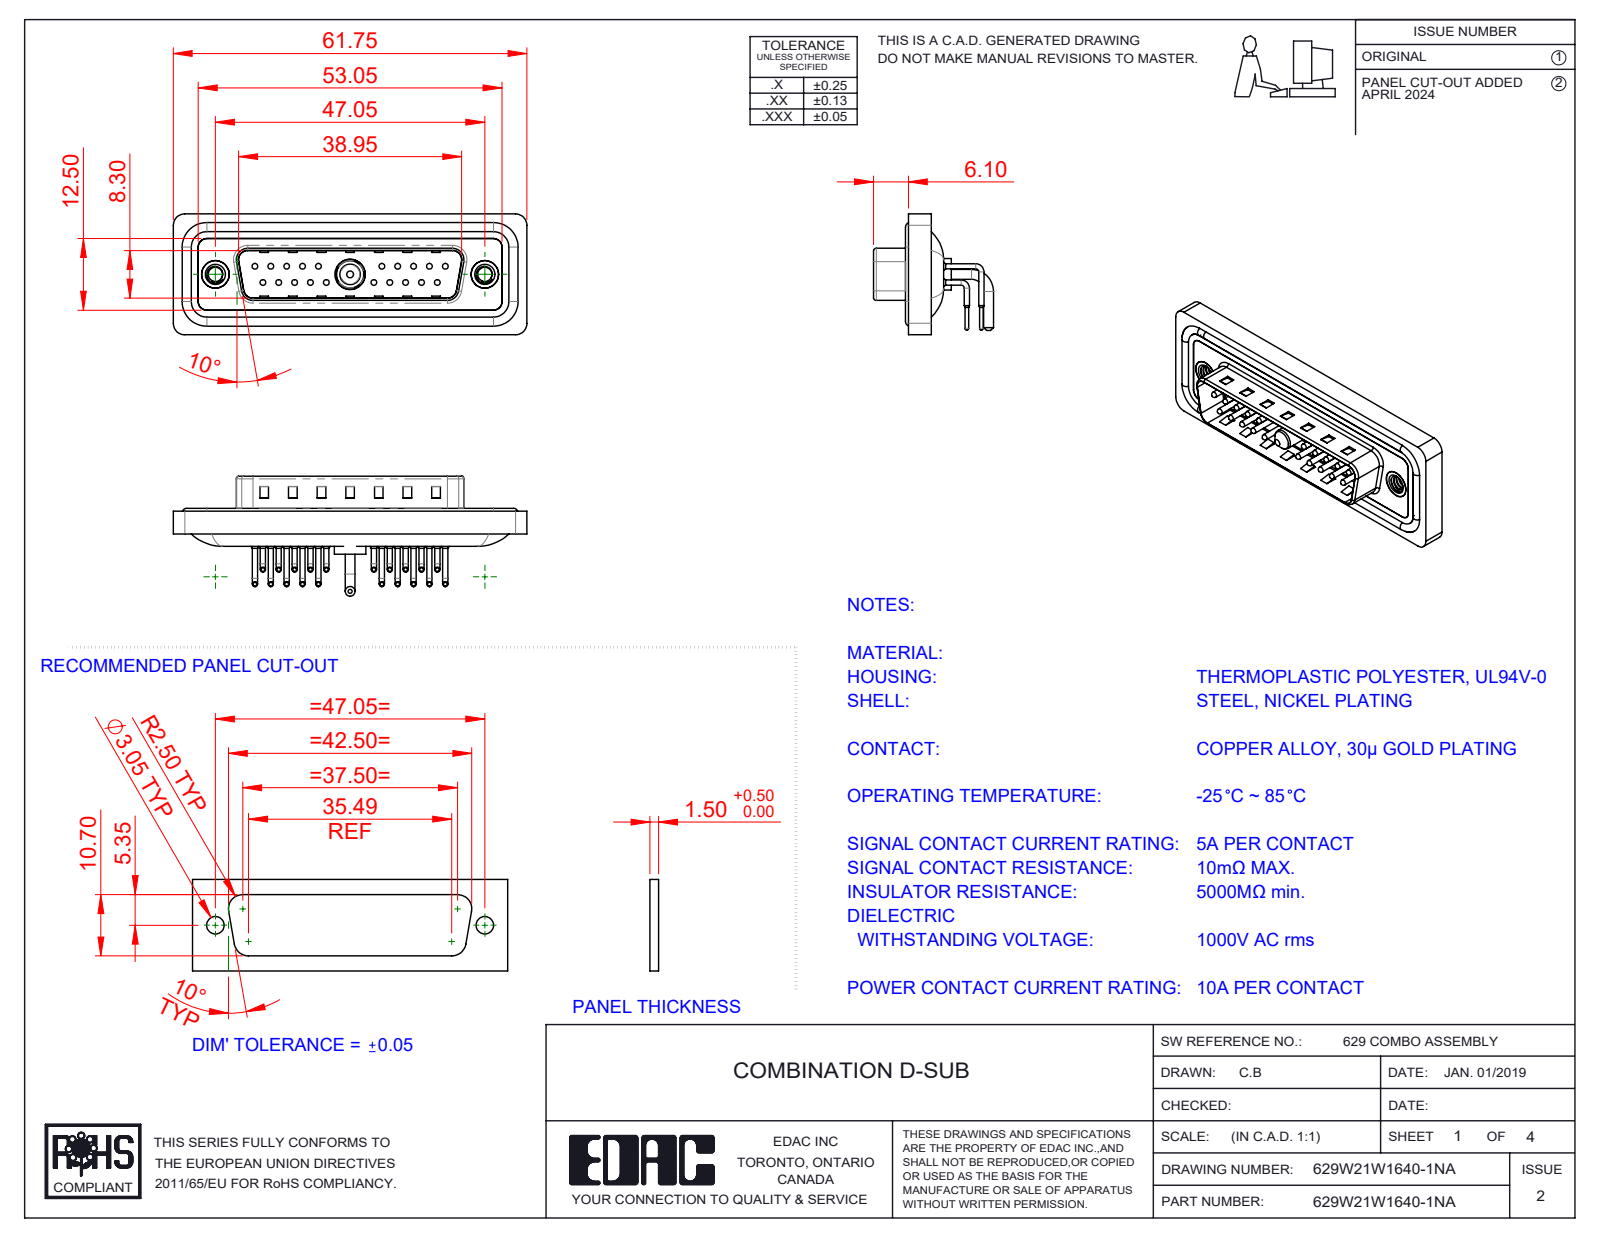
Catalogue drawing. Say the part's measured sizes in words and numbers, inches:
The part is named "629Combo Housing_21W1; 629Combo Contact Row 2; 629Combo Shell Rear_25 Contacts; 629Combo Contact Row 1 (+5 more)". Its 3-D file was written by "SolidWorks 2023 (CONFIG_CONTROL_DESIGN)". It is 29 solids with 2720 faces: 1499 planar, 927 cylindrical and 294 other. Overall it measures 2.431 by 0.831 by 0.825 inches. Its volume is 0.449 cubic inches and its surface area 19.64 square inches. Round holes: 20 of diameter 0.03, 20 of diameter 0.063, 20 of diameter 0.079, 2 of diameter 0.098, 2 of diameter 0.157, 2 of diameter 0.189, 2 of diameter 0.197, 1 of diameter 0.191, 1 of diameter 0.209. Round bosses or shafts: 40 of diameter 0.035, 20 of diameter 0.059, 20 of diameter 0.039, 20 of diameter 0.026, 4 of diameter 0.063, 2 of diameter 0.193, 2 of diameter 0.067, 1 of diameter 0.217. Partial cylindrical surfaces (rounded edges, fillets, slot ends): 20 of radius 0.04, 18 of radius 0.059, 18 of radius 0.079, 8 of radius 0.02, 8 of radius 0.063, 4 of radius 0.01, 4 of radius 0.024, 4 of radius 0.026. The main face-to-face distances are 0.016, 0.114, 0.031, 0.161, 0.043, 0.083, 0.063, 0.177, 0.059, 0.098. The hole center spacings are 0.124, 0.109, 0.218, 0.327, 0.198, 0.763, 0.826, 0.872.
